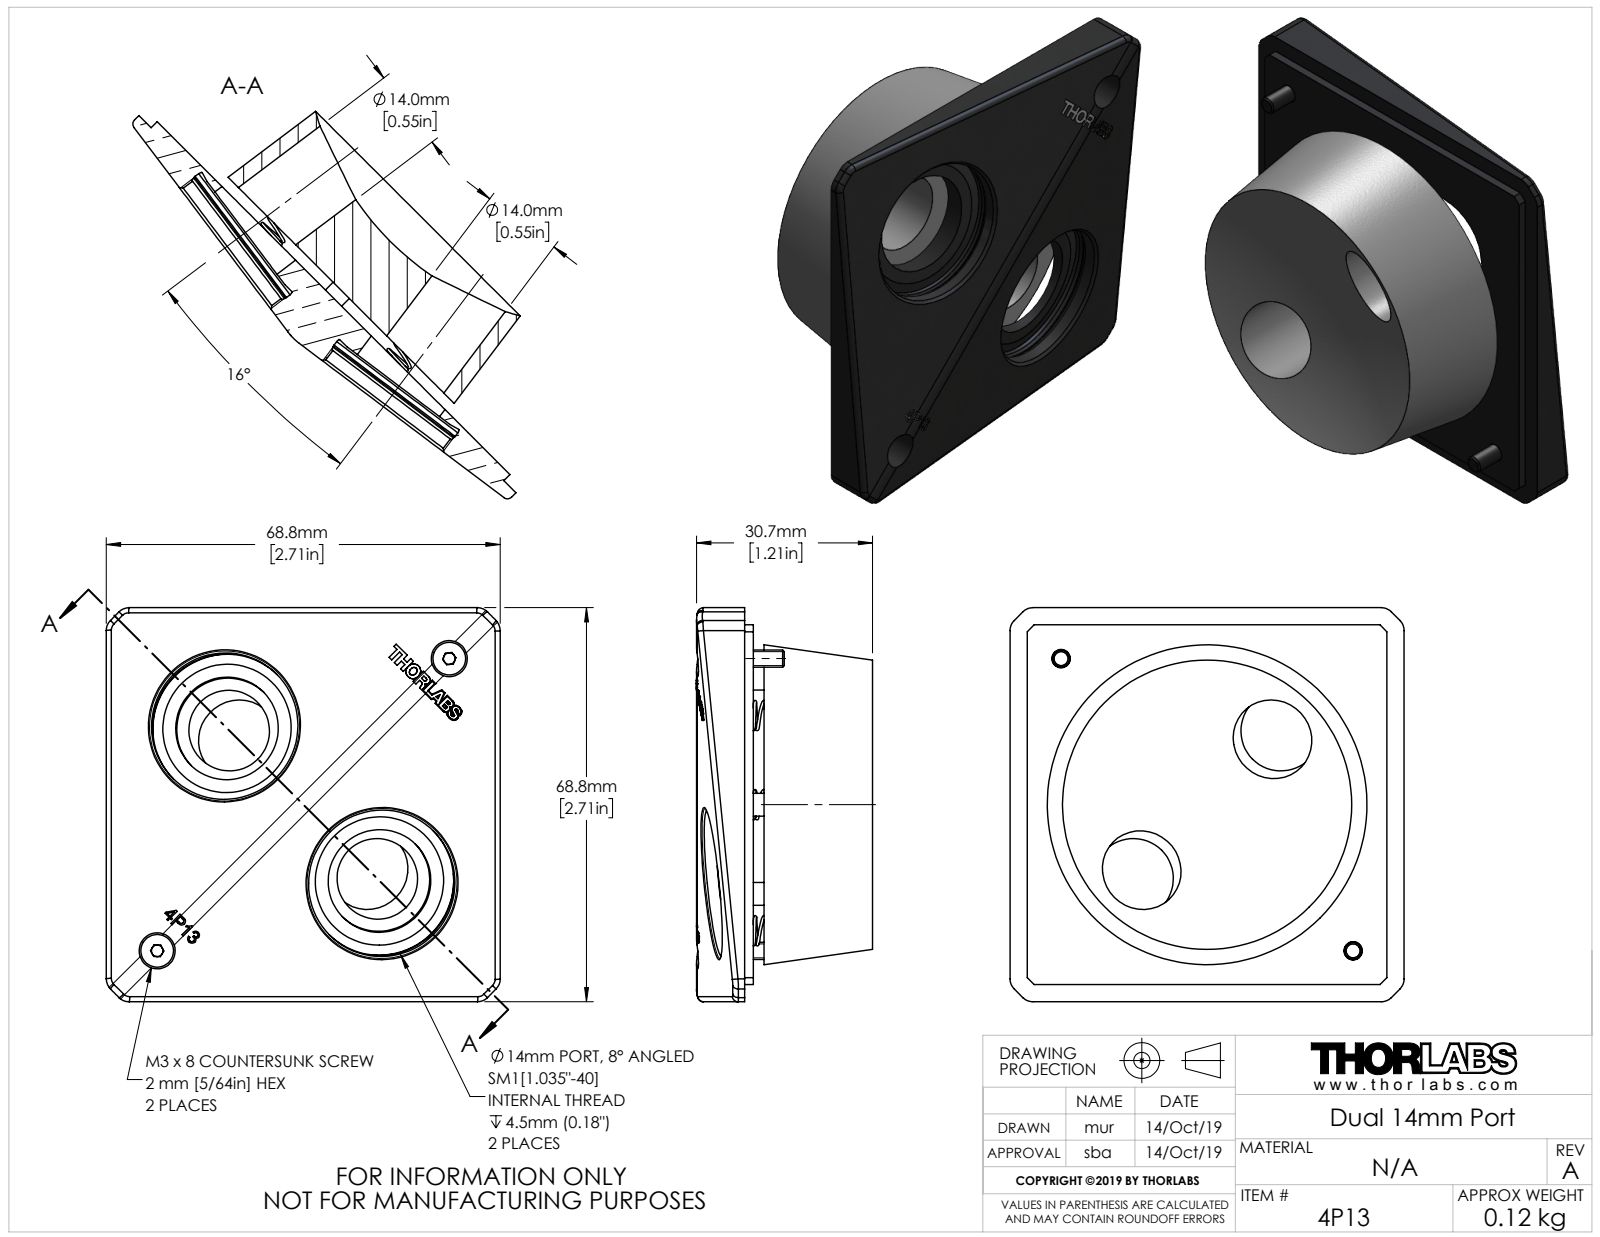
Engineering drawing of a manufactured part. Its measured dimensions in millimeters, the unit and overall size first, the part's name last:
Units: millimetres
Overall size (bounding box): 68.8 × 68.8 × 30.75
Round holes (diameter × count): ⌀4 ×3, ⌀4.5 ×3, ⌀5.5 ×3, ⌀6.5 ×3, ⌀3.2 ×2, ⌀6.3 ×2, ⌀14 ×2, ⌀18 ×2, ⌀25.68 ×2, ⌀26.48 ×1, ⌀26.48 ×1
Round bosses / shafts (diameter × count): ⌀5.5 ×3, ⌀5.7 ×2, ⌀3 ×2
Partial cylindrical surfaces — rounded edges, fillets, slot ends (radius × count): R2.5 ×8, R1 ×6, R9.99 ×1, R10 ×1
Main face-to-face distances: 1.9, 3.4, 1.5, 68.8, 3, 65.8, 62.8, 4.54, 4.51, 4.4
Hole centre spacings: 16.84, 25.74, 31.11, 40.66, 53.91, 14.06, 44, 58.07
Volume: 58 428 mm³ · Surface area: 21 998 mm²
Bodies: 10 solids, 823 faces (597 planar, 92 cylindrical, 134 other)
Part name (STEP PRODUCT): 19.11.04_4P13_IS Dual Port WEB
STEP written by: SolidWorks 2018 (AUTOMOTIVE_DESIGN)
